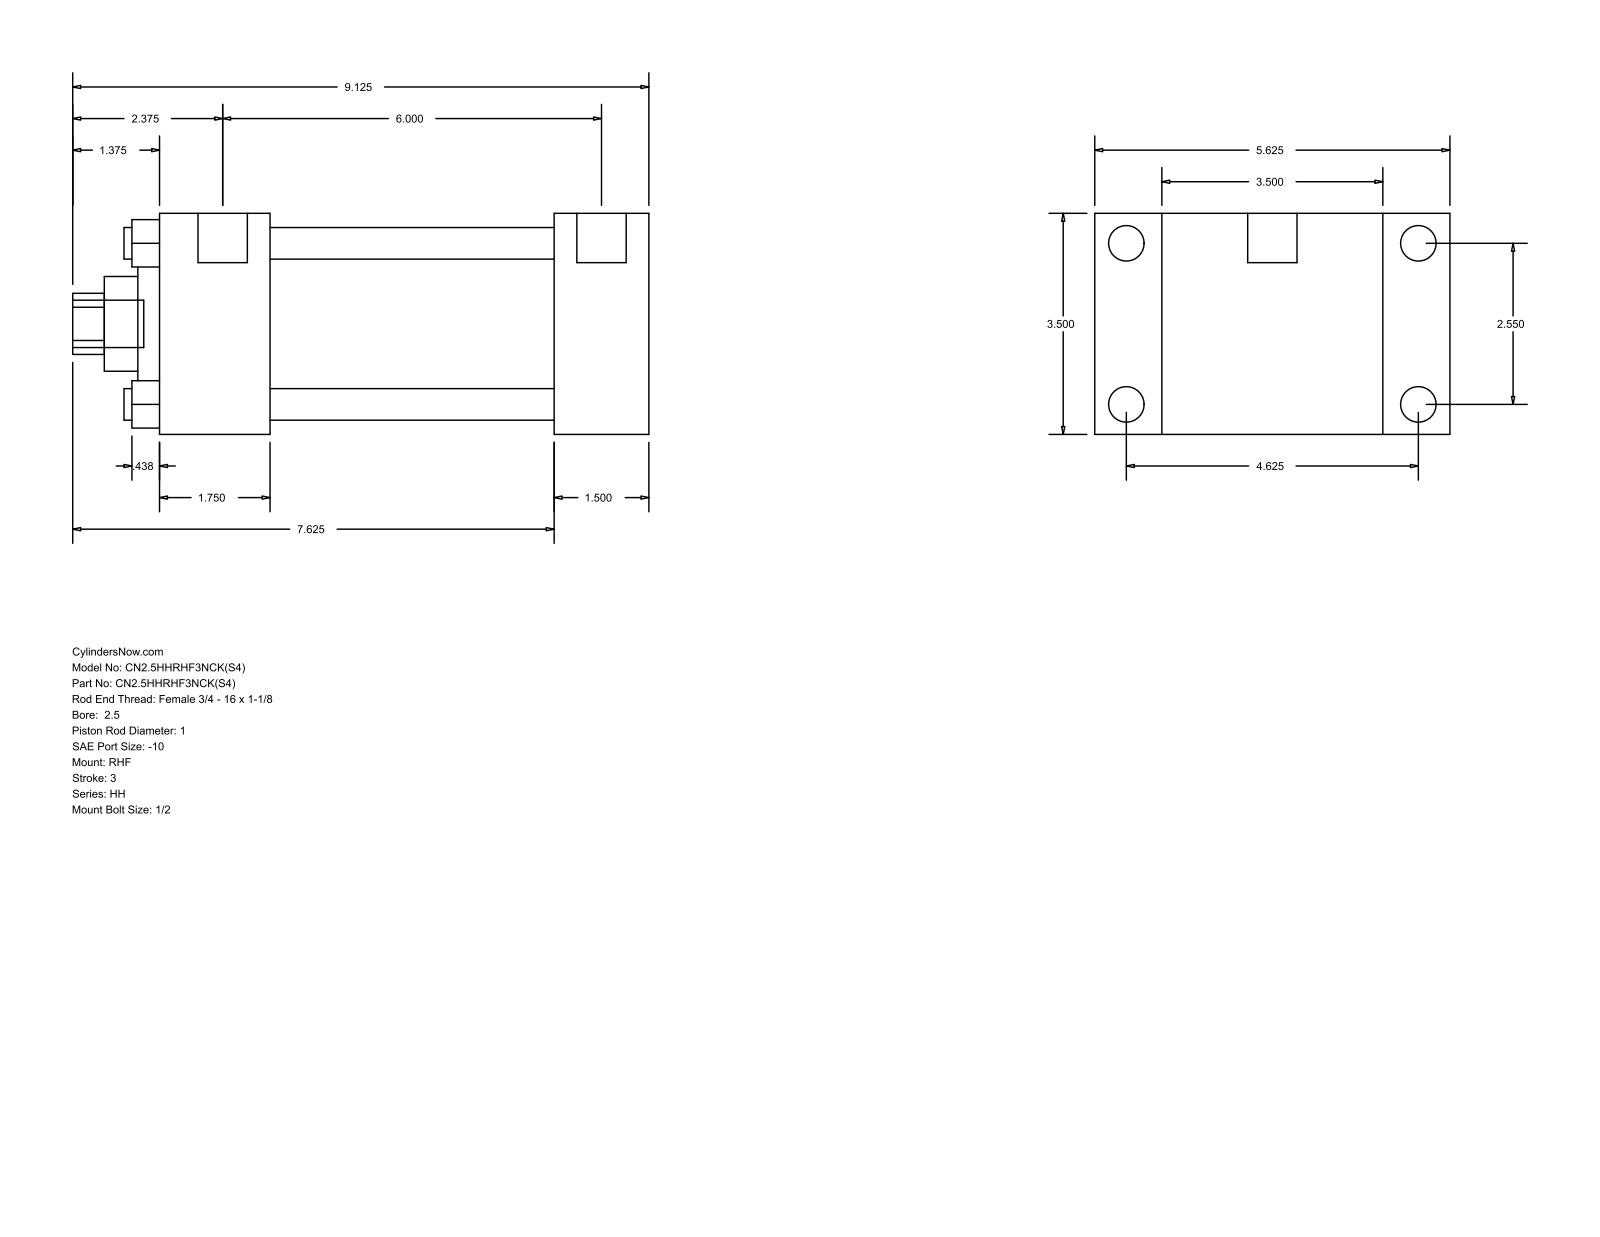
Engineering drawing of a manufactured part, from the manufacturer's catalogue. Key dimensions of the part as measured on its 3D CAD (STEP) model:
Part name (STEP PRODUCT): HH_RHF__0250_1
STEP written by: GSSL Pune (CONFIG_CONTROL_DESIGN)
Units: millimetres
Bodies: 0 solids, 90 faces (61 planar, 29 cylindrical, 0 other)
Overall size (bounding box): 231.78 × 142.88 × 88.9
Round holes (diameter × count): ⌀12.7 ×4, ⌀25.4 ×1, ⌀38.1 ×1, ⌀60.33 ×1, ⌀73.03 ×1
Round bosses / shafts (diameter × count): ⌀14.3 ×4, ⌀5.56 ×4, ⌀19.84 ×2, ⌀19.05 ×1
Partial cylindrical surfaces — rounded edges, fillets, slot ends (radius × count): R12.29 ×1
Main face-to-face distances: 88.9, 38.1, 26.99, 115.89, 158.76, 196.86, 142.88, 44.46, 114.3, 152.4
Hole centre spacings: 45.79, 64.76, 91.58
